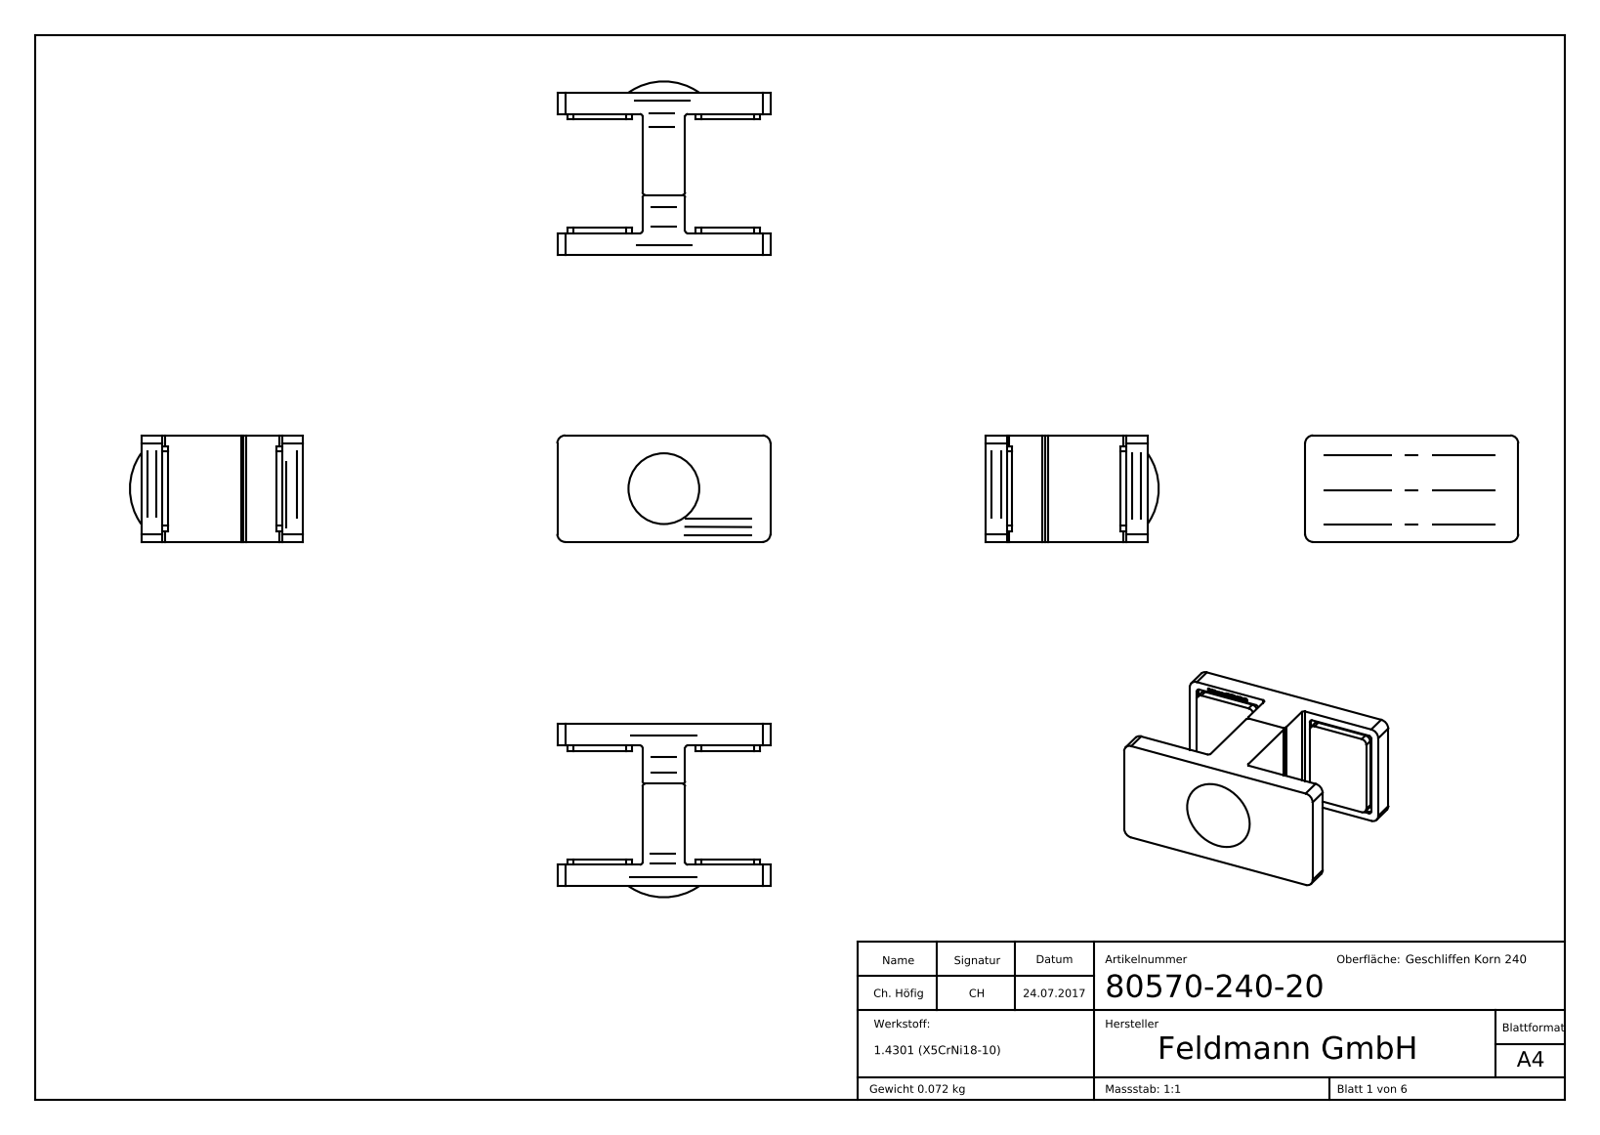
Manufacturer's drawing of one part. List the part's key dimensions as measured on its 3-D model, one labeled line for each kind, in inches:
Part name (STEP PRODUCT): DIN7991 M6xXX_DIN7991 M6x25; 80570-XXX-XX Teil2; 80570-XXX-XX Teil1; 80570-XXX-XX Teil2_80570-240-20 Teil2 (+7 more)
STEP written by: SolidWorks 2018 (CONFIG_CONTROL_DESIGN)
Units: inches
Bodies: 8 solids, 829 faces (378 planar, 203 cylindrical, 248 other)
Overall size (bounding box): 1.575 × 1.28 × 0.787
Volume: 0.635 in³ · Surface area: 14.35 in²
Round holes (diameter × count): ⌀0.106 ×2, ⌀0.071 ×1, ⌀0.197 ×1, ⌀0.256 ×1, ⌀0.492 ×1
Round bosses / shafts (diameter × count): ⌀0.472 ×1, ⌀0.236 ×1, ⌀0.157 ×1
Partial cylindrical surfaces — rounded edges, fillets, slot ends (radius × count): R0.02 ×80, R0.008 ×12, R0.039 ×8, R0.007 ×4, R0.059 ×4
Main face-to-face distances: 0.138, 1.059, 0.059, 0.197, 1.197, 1, 0.862, 0.921, 0.079, 0.315
Hole centre spacings: 0.256, 0.512
